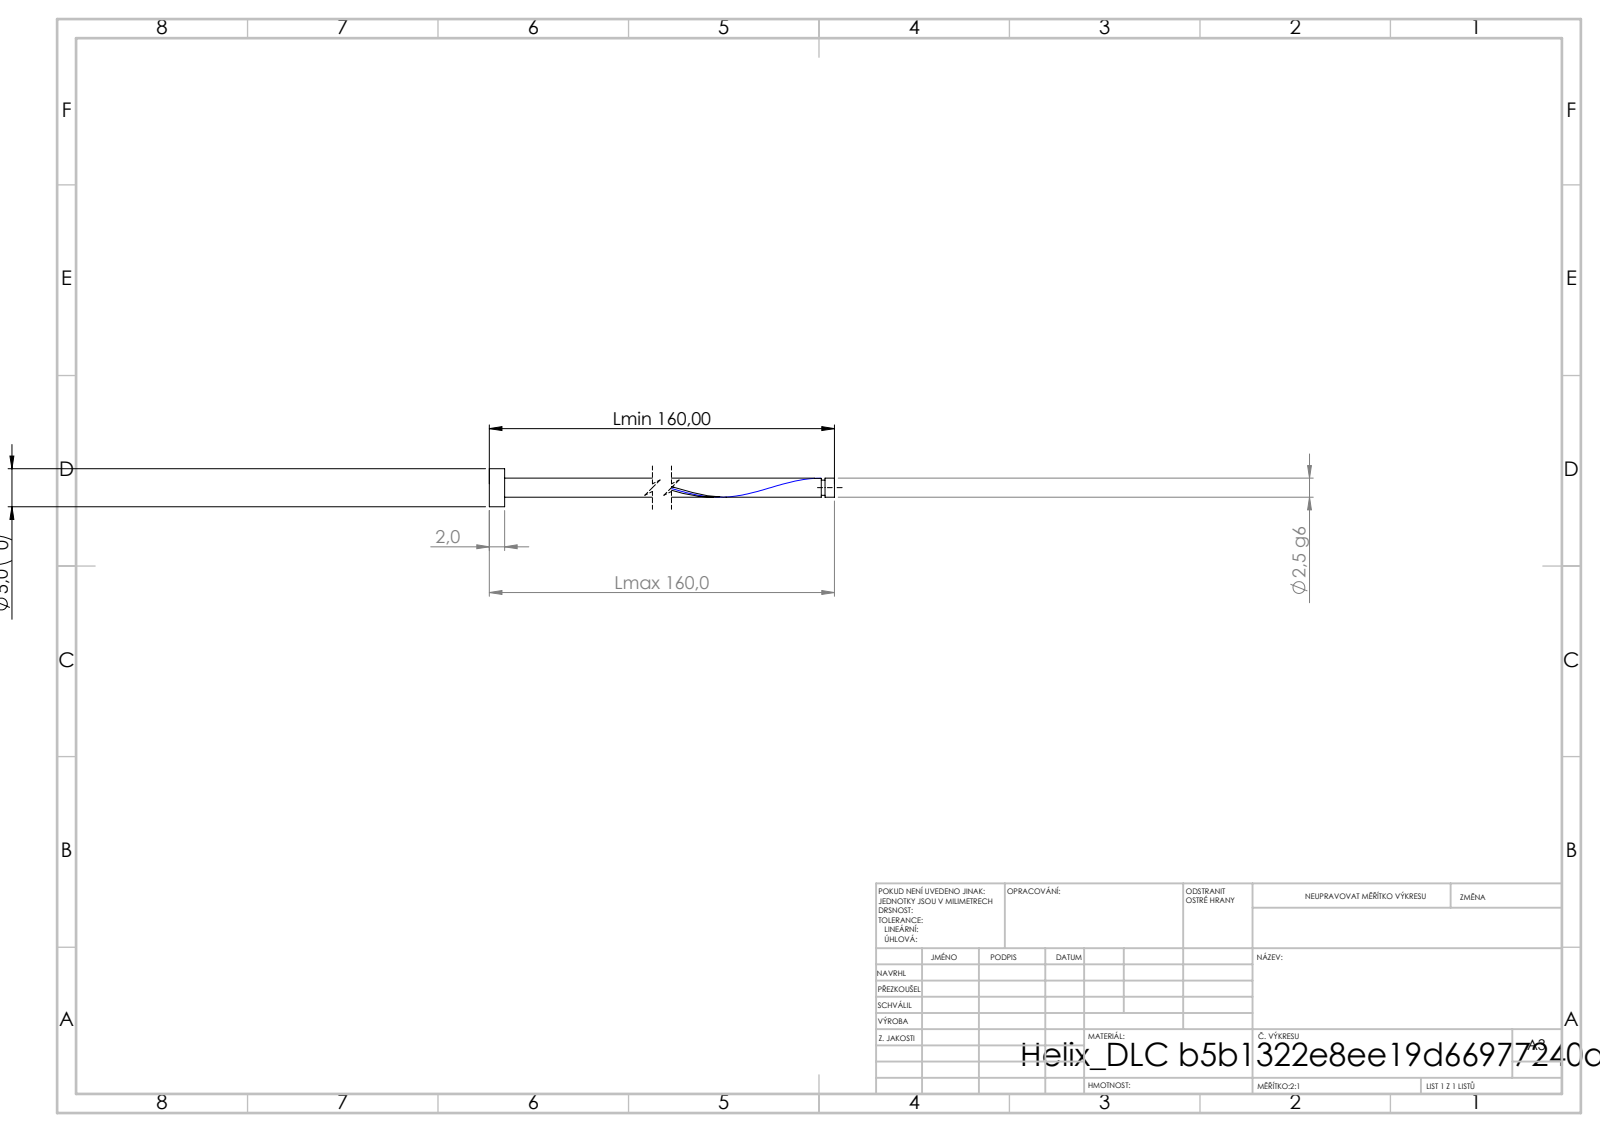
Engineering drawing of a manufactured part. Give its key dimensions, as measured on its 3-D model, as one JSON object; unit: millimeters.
{"step_written_by": "SolidWorks 2019 (CONFIG_CONTROL_DESIGN)", "units": "millimeters", "bodies": {"solids": 1, "faces": 16, "planar": 6, "cylindrical": 9, "other": 1}, "overall_size": [160, 5, 5], "volume_mm3": 981, "surface_area_mm2": 1753, "round_bosses_or_shafts": [[5, 1], [2.5, 1], [2, 1]], "face_to_face_distances": [2, 160, 158, 158.76, 156.76, 1.24, 158.26, 156.26, 0.5, 1.74]}
